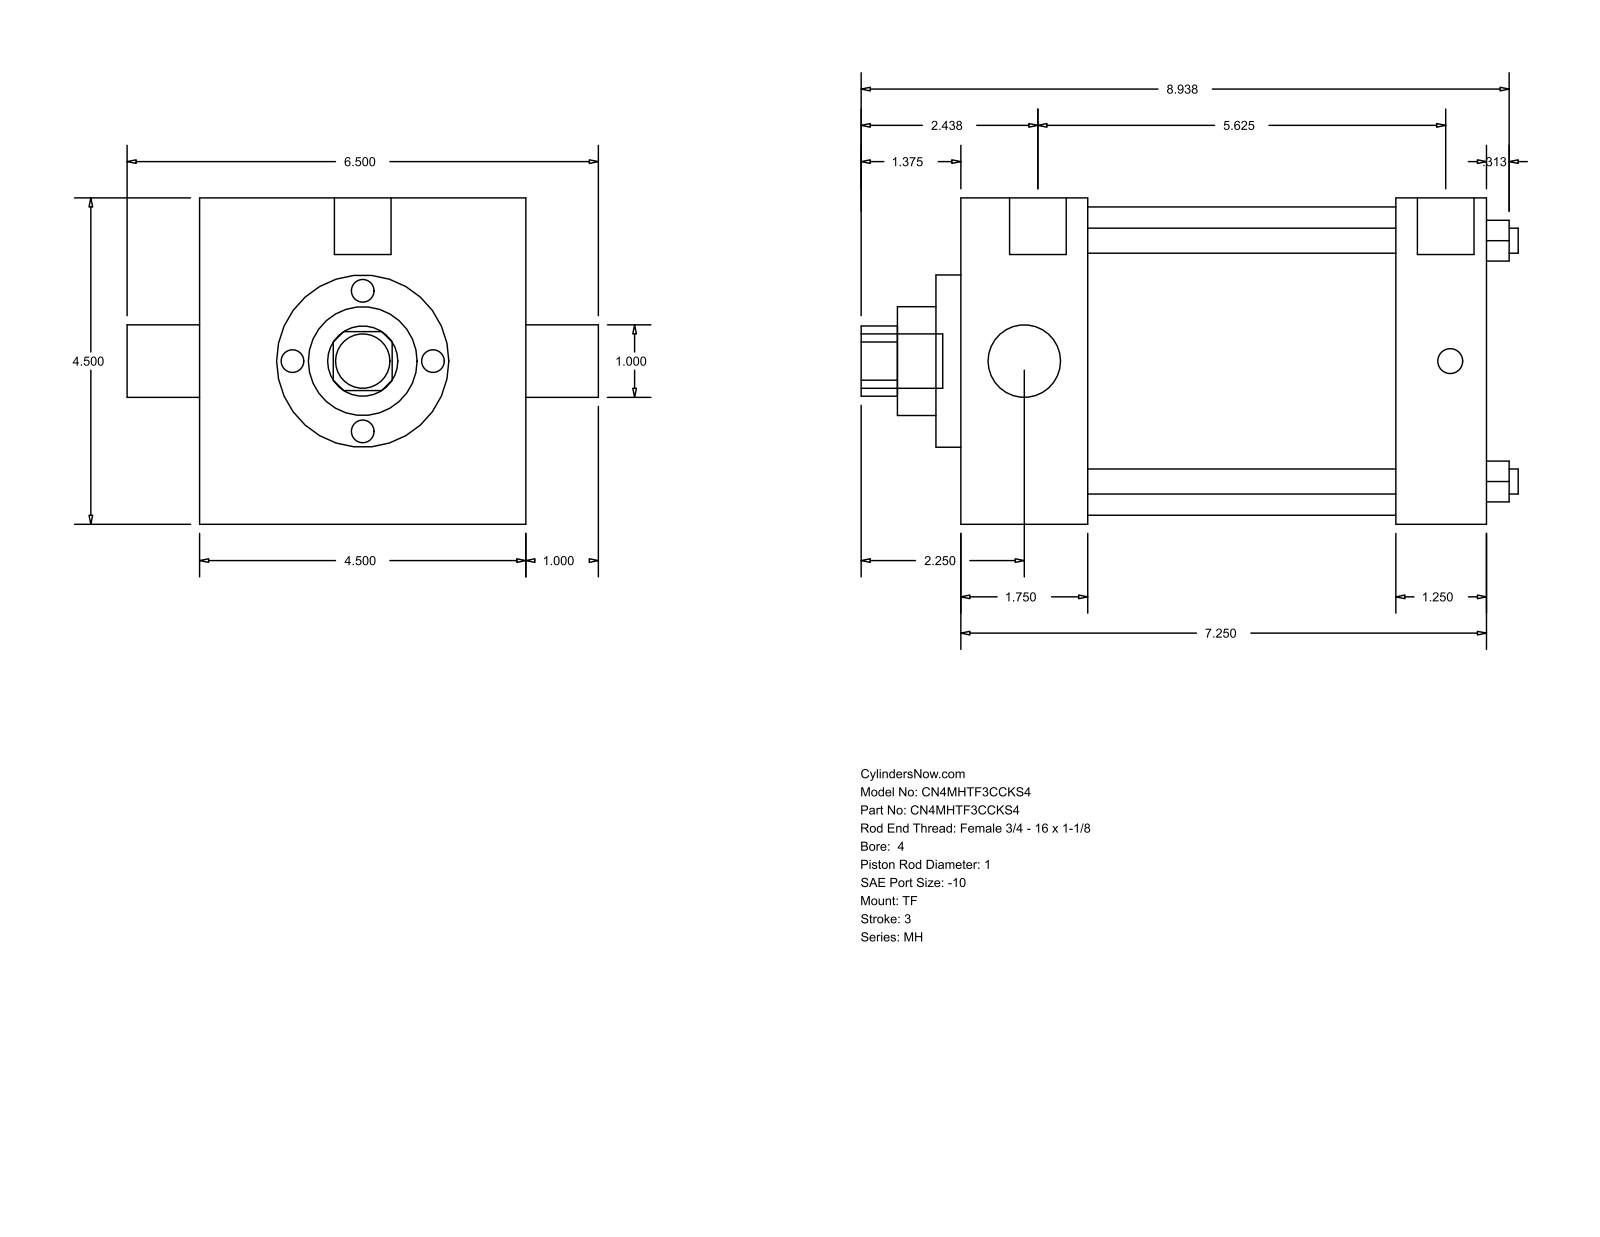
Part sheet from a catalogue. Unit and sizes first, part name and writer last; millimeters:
Units: millimetres
Overall size (bounding box): 230.19 × 165.1 × 114.3
Round holes (diameter × count): ⌀8.76 ×4, ⌀25.4 ×2, ⌀38.1 ×1, ⌀60.33 ×1, ⌀107.95 ×1
Round bosses / shafts (diameter × count): ⌀8.73 ×3, ⌀19.84 ×2, ⌀19.05 ×1
Partial cylindrical surfaces — rounded edges, fillets, slot ends (radius × count): R12.29 ×1
Main face-to-face distances: 114.3, 184.15, 44.46, 139.69, 152.4, 107.94, 31.75, 8.73, 53.19, 161.13
Hole centre spacings: 59.62, 84.32, 119.25
Bodies: 0 solids, 86 faces (61 planar, 25 cylindrical, 0 other)
Part name (STEP PRODUCT): MH_TF__0400_1
STEP written by: GSSL Pune (CONFIG_CONTROL_DESIGN)
